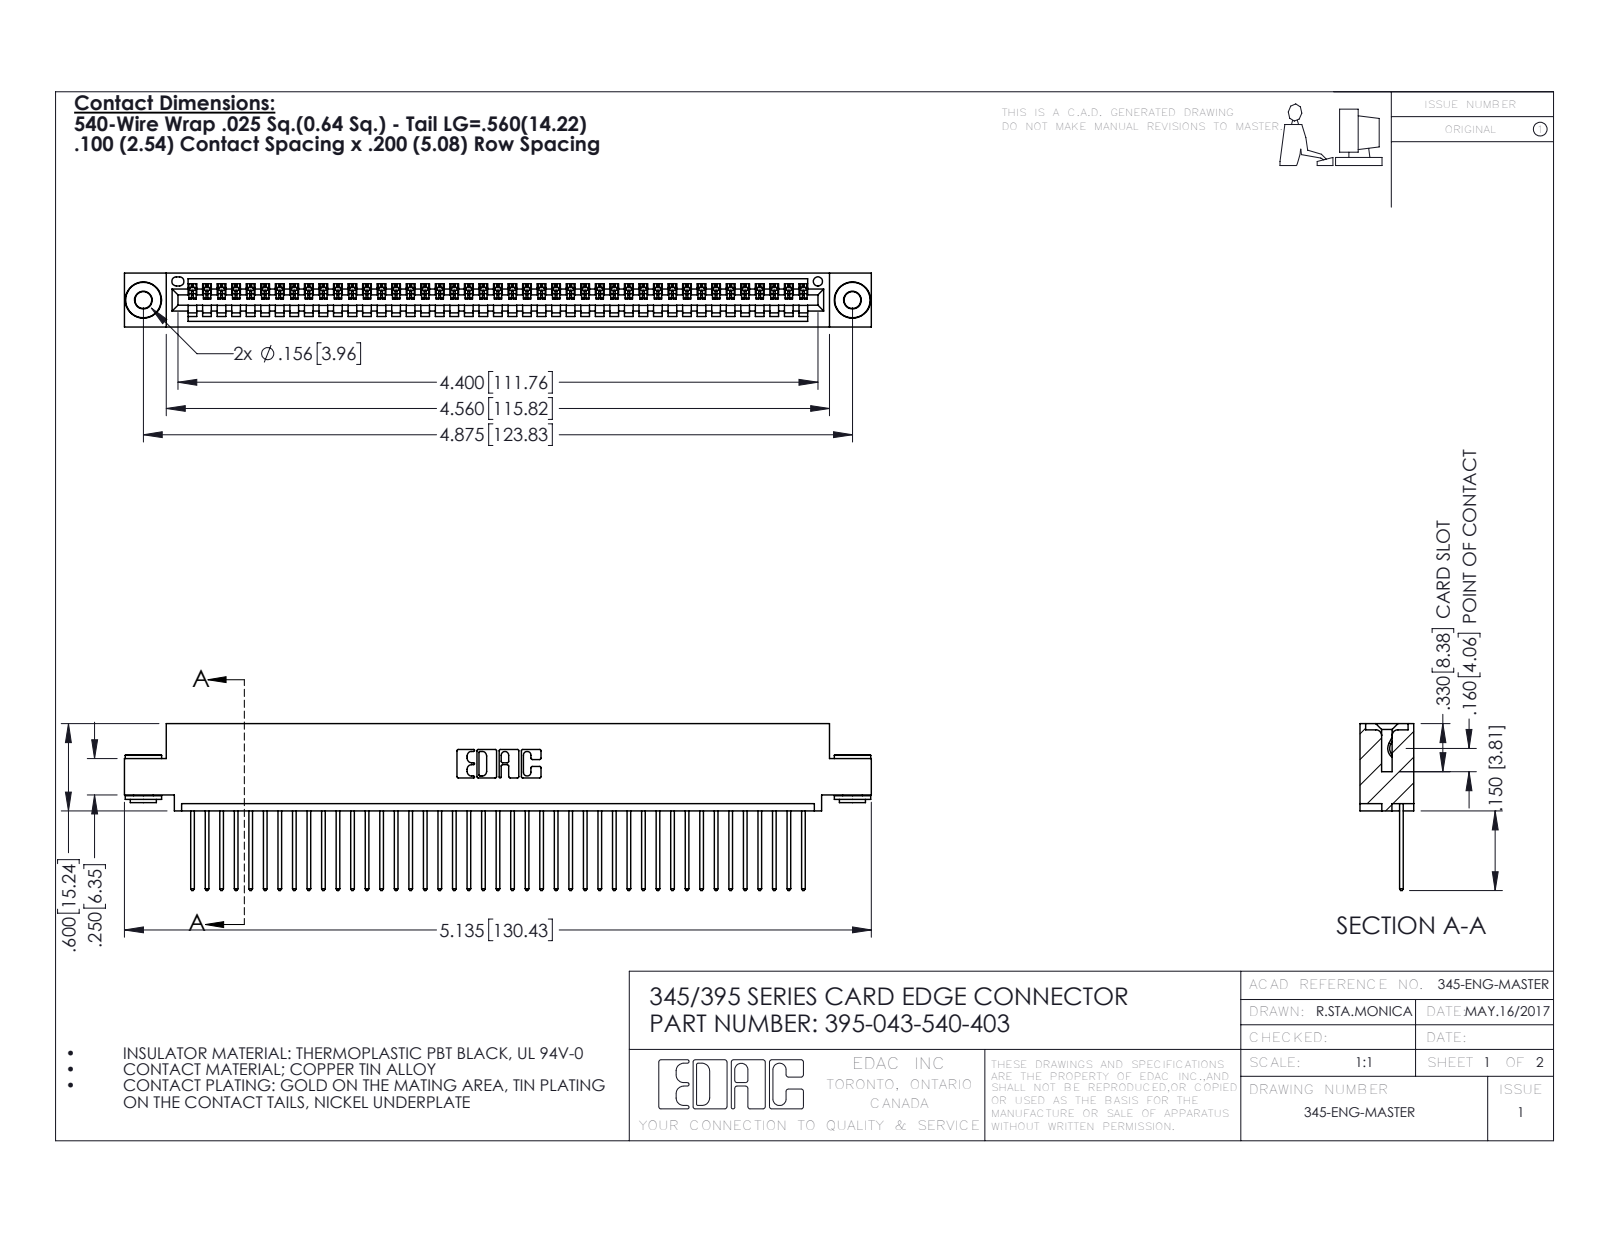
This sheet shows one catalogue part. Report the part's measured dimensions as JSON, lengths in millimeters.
{"part_name": "395-043-540-403; 345-250-002_345-250-002-102; 345-292-001_345-293-140; 345 Part_0.110 Offset - 0.156 Dia-TH", "step_written_by": "SolidWorks 2016 (CONFIG_CONTROL_DESIGN)", "units": "millimeters", "bodies": {"solids": 46, "faces": 2662, "planar": 1814, "cylindrical": 840, "other": 8}, "overall_size": [130.4, 29.1, 9.4], "volume_mm3": 12400, "surface_area_mm2": 17210, "round_holes": [[2.9, 2], [4, 2], [1.6, 1]], "round_bosses_or_shafts": [[6.4, 2], [4.6, 2], [3.5, 2]], "partial_cylinders_radius": [[0.2, 86], [0.3, 86], [0.3, 22], [0.2, 6], [0.8, 6], [0.7, 3], [0.8, 2], [1, 2]], "face_to_face_distances": [1.8, 7.6, 0.6, 9.4, 2.5, 6.9, 5.1, 5.7, 3.8, 1.8], "hole_center_spacings": [6.9, 117.8, 123.8]}
